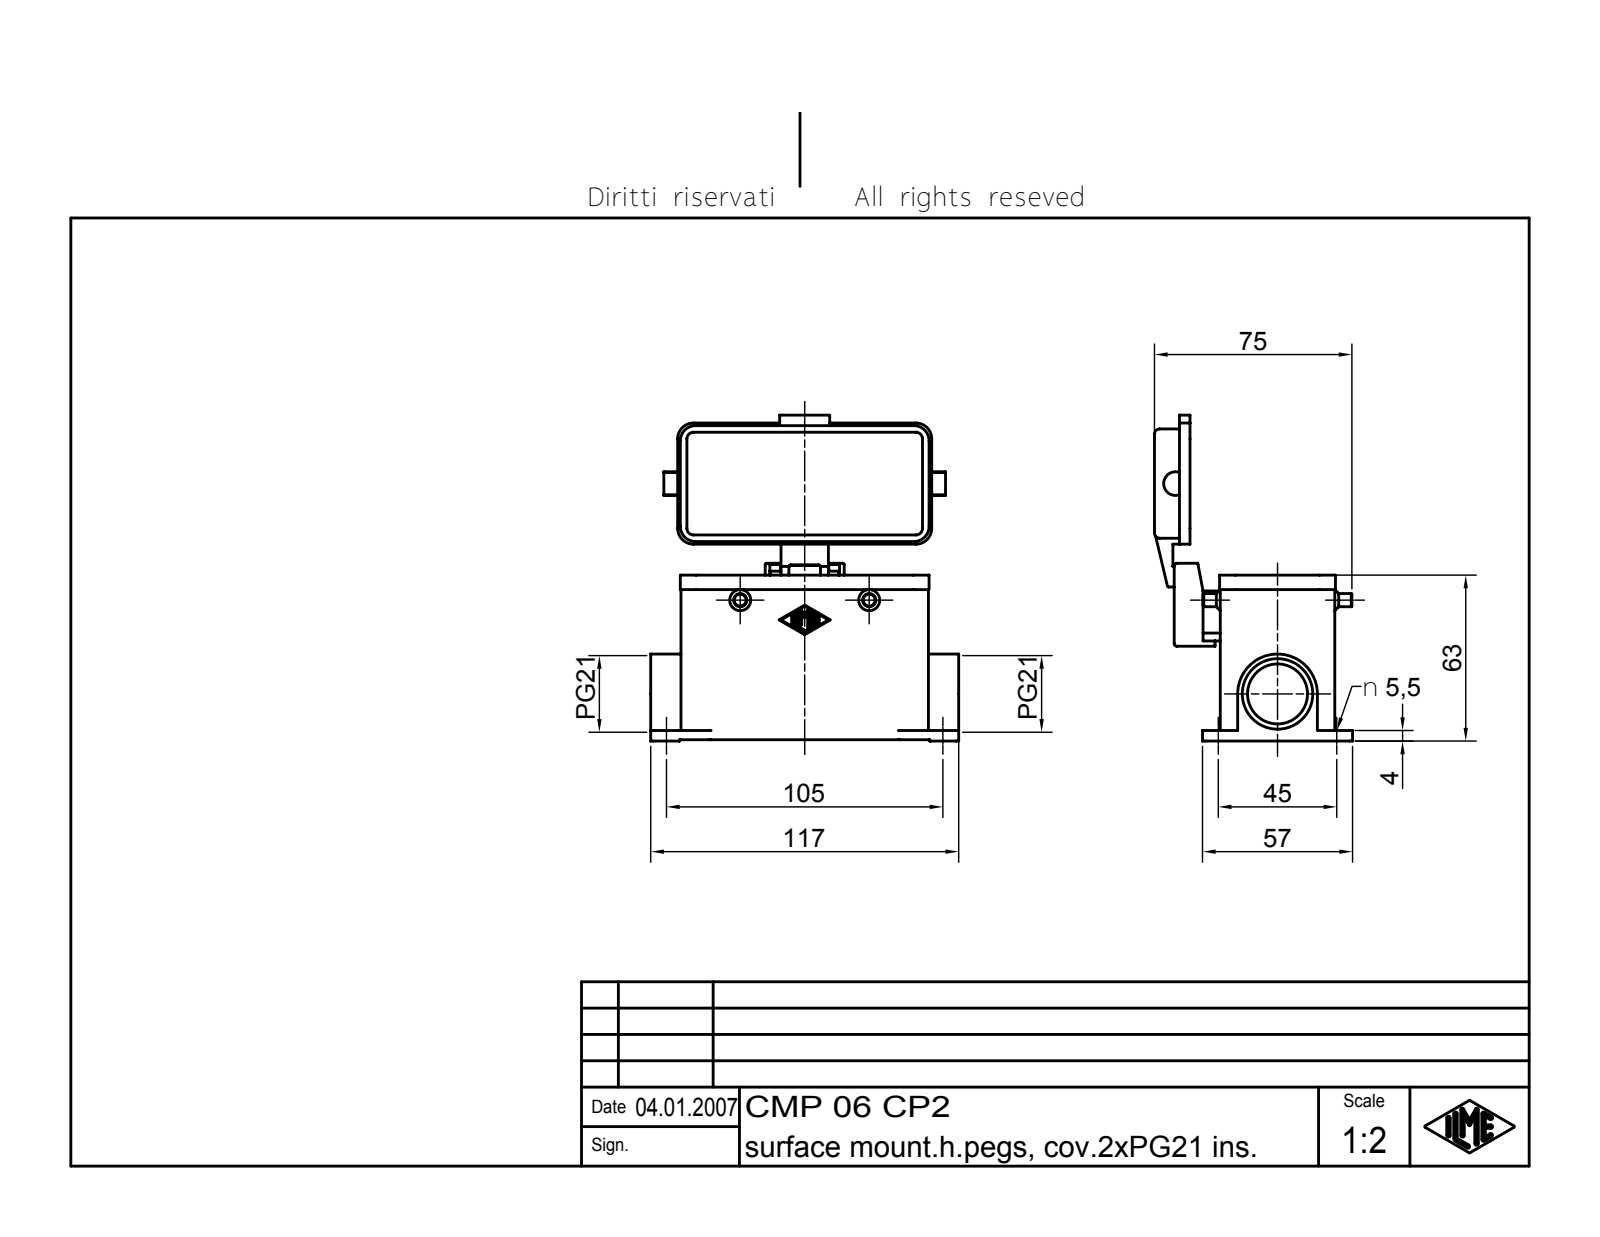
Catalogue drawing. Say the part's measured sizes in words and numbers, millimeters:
The part is named "CMP 06 CP2". Its 3-D file was written by "Autodesk Inventor 7 (AUTOMOTIVE_DESIGN)". It is 1 solid with 469 faces: 195 planar, 164 cylindrical and 110 other. Overall it measures 123.75 by 117 by 75.25 millimeters. Its volume is 108 626 cubic millimeters and its surface area 67 349 square millimeters. Round holes: 4 of diameter 5.5, 1 of diameter 4, 1 of diameter 5, 1 of diameter 22.78, 1 of diameter 26.78. Round bosses or shafts: 2 of diameter 5, 2 of diameter 3, 1 of diameter 7, 1 of diameter 4. Partial cylindrical surfaces (rounded edges, fillets, slot ends): 14 of radius 0.38, 14 of radius 1, 12 of radius 6, 10 of radius 0.5, 8 of radius 0.7, 8 of radius 2, 4 of radius 2.5, 4 of radius 3. The main face-to-face distances are 3, 40.5, 43.5, 2.5, 63, 37.5, 3.5, 22.5, 66, 25.5. The hole center spacings are 45, 105, 114.24.
